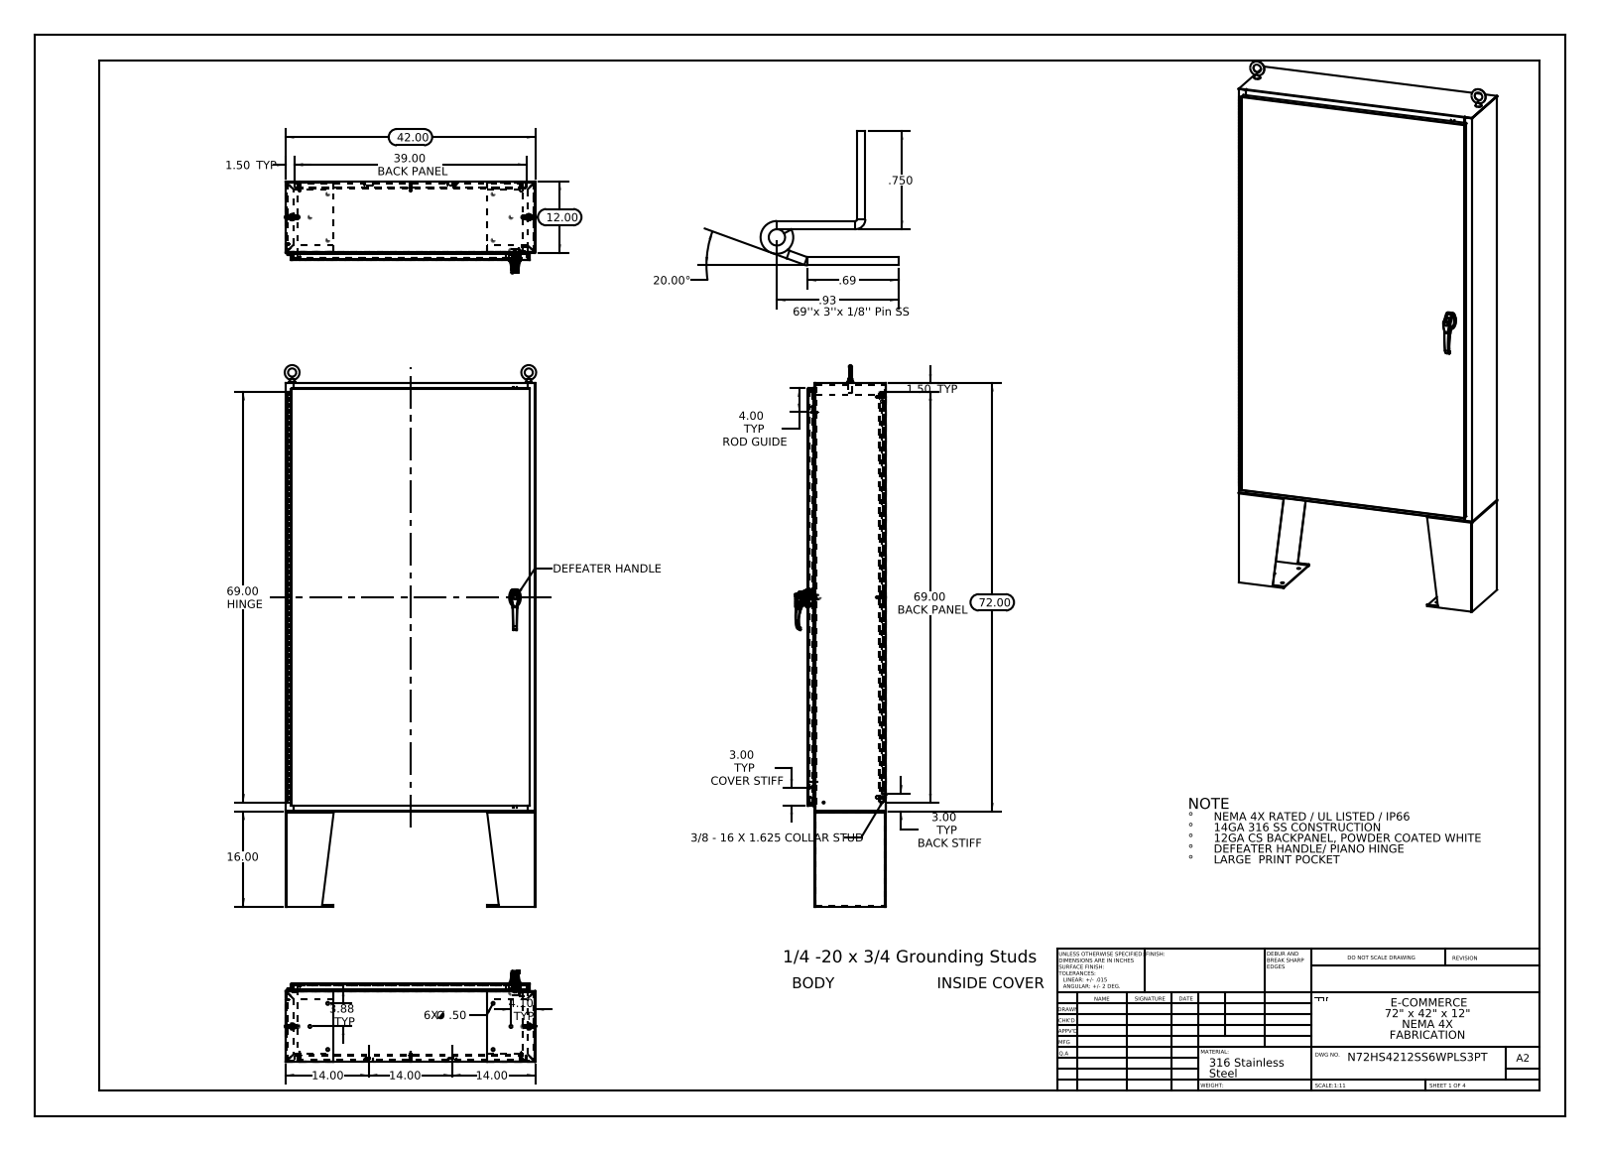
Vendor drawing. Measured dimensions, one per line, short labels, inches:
name: N72HS4212SSWPLS3PT Defeater Handle - 3 - 2500-51 ZN; N72HS4212SSWPLS3PT Backpanel; 00005310_26163101; N72HS4212SSWPLS3PT (+8 more)
written by: SolidWorks 2013 (CONFIG_CONTROL_DESIGN)
unit: in
bodies: 55 solids, 4096 faces (1673 planar, 1605 cylindrical, 818 other)
size: 91 × 42.271 × 15.307
volume: 1 190 in³; area: 28 671 in²
holes: 14× ⌀0.5, 10× ⌀0.25, 4× ⌀0.75, 3× ⌀0.138, 3× ⌀0.161, 2× ⌀0.079, 2× ⌀0.203, 2× ⌀0.313, 2× ⌀0.437, 1× ⌀0.125, 1× ⌀0.125, 1× ⌀0.197
bosses: 10× ⌀0.625, 10× ⌀0.157, 10× ⌀0.14, 8× ⌀0.375, 8× ⌀0.33, 3× ⌀0.315, 3× ⌀0.236, 1× ⌀1.181
rounds: 37× R0.118, 34× R0.013, 33× R0.006, 28× R0.088, 15× R0.039, 12× R0.028, 8× R0.039, 8× R0.143
face distances: 0.075, 13.126, 0.104, 13.051, 1.075, 13.201, 1, 12.051, 12.126, 1.179
hole spacings: 7.137, 16.578, 29.353, 31.035, 31.661, 33.625, 34.004, 34.006
